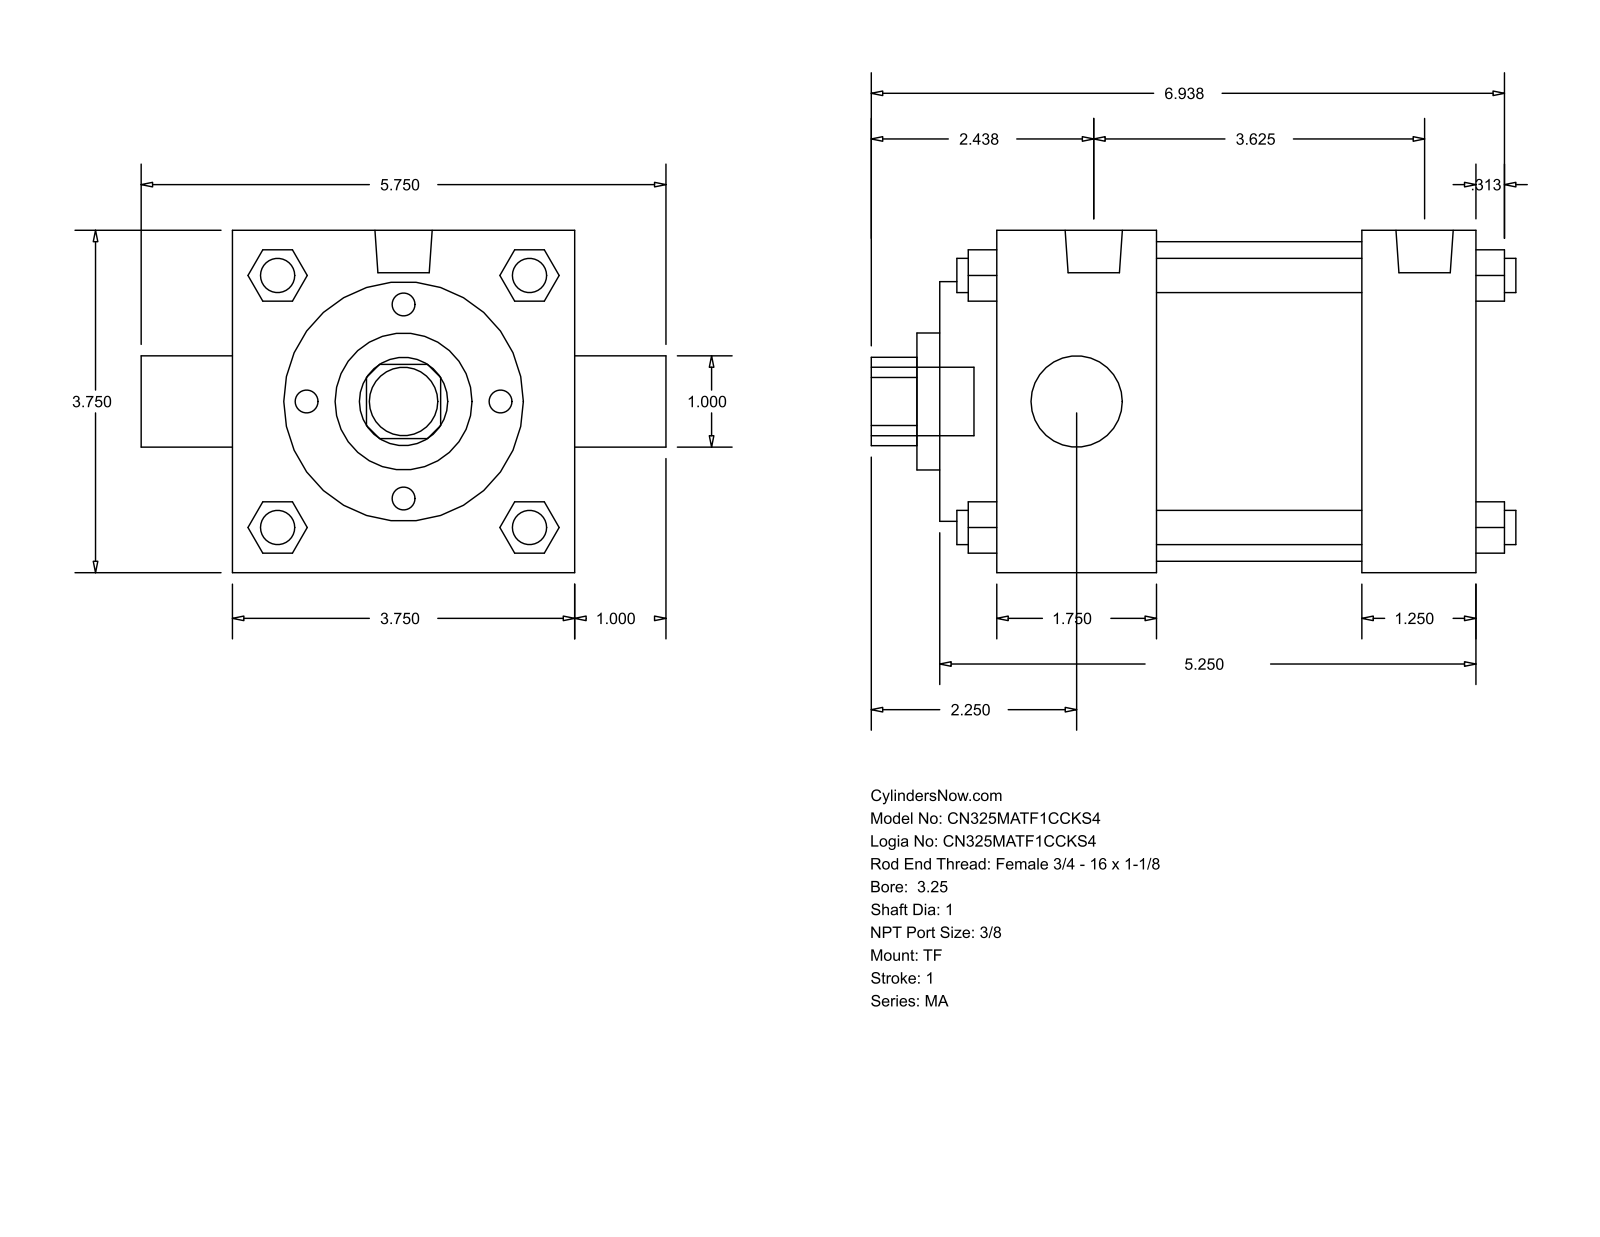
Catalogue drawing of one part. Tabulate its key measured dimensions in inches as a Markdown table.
| quantity | value |
| --- | --- |
| part name | MA_TF__0325_1 |
| STEP written by | GSSL Pune (CONFIG_CONTROL_DESIGN) |
| units | inches |
| bodies | 0 solids, 122 faces (93 planar, 29 cylindrical, 0 other) |
| overall size | 7.063 × 5.75 × 3.75 |
| round holes (diameter × count) | 1 × 2, 1.5 × 1, 2.625 × 1, 3.5 × 1 |
| round bosses / shafts (diameter × count) | 0.375 × 4, 0.437 × 3, 0.627 × 2, 0.75 × 1 |
| partial cylindrical surfaces (radius × count) | 0.484 × 1 |
| main face-to-face distances | 3.75, 5.25, 0.625, 1.75, 4, 2.25, 3.5, 1.25, 2.375, 4.625 |
